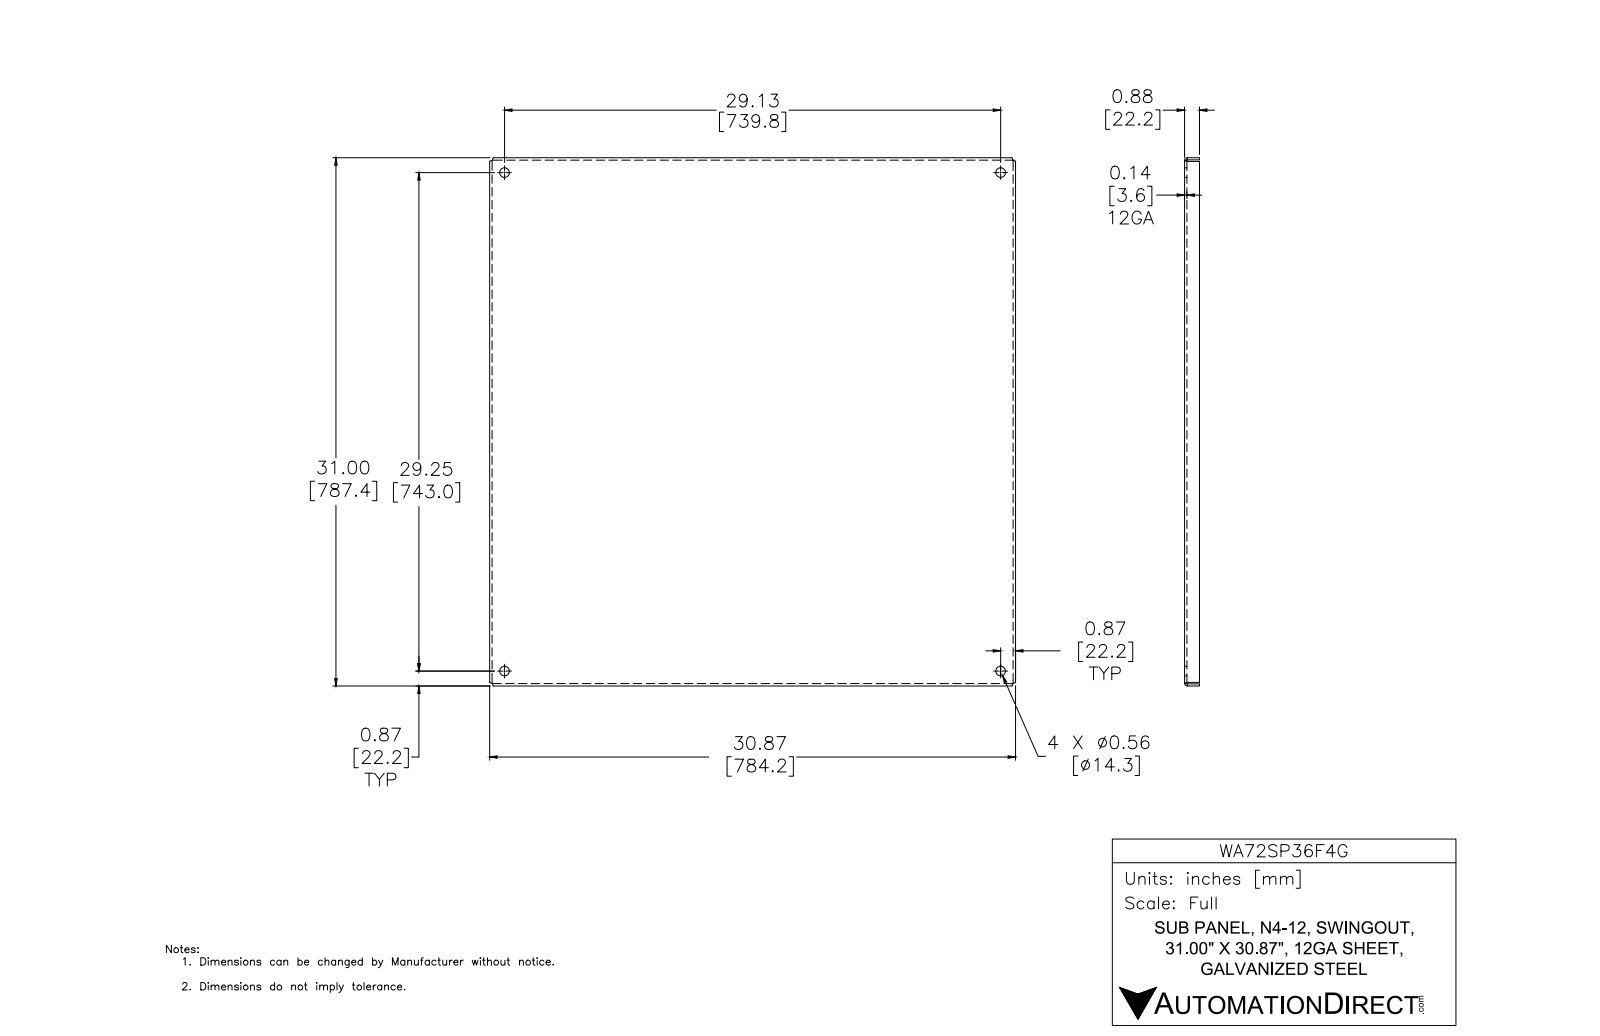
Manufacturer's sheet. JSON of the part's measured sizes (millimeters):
{"part_name": "WA60SP24F3G-WA90SP36F4G", "step_written_by": "Autodesk Inventor 2012 (AUTOMOTIVE_DESIGN)", "units": "millimeters", "bodies": {"solids": 1, "faces": 42, "planar": 22, "cylindrical": 12, "other": 8}, "overall_size": [787.4, 784.4, 22.2], "volume_mm3": 1610000, "surface_area_mm2": 1360000, "round_holes": [[14.3, 4]], "partial_cylinders_radius": [[0.8, 4], [3.2, 4]], "face_to_face_distances": [2.4, 782, 785, 784.4, 779.6, 787.4, 782.7, 19.8, 22.2, 4.1], "hole_center_spacings": [739.9, 743, 1048.5]}
